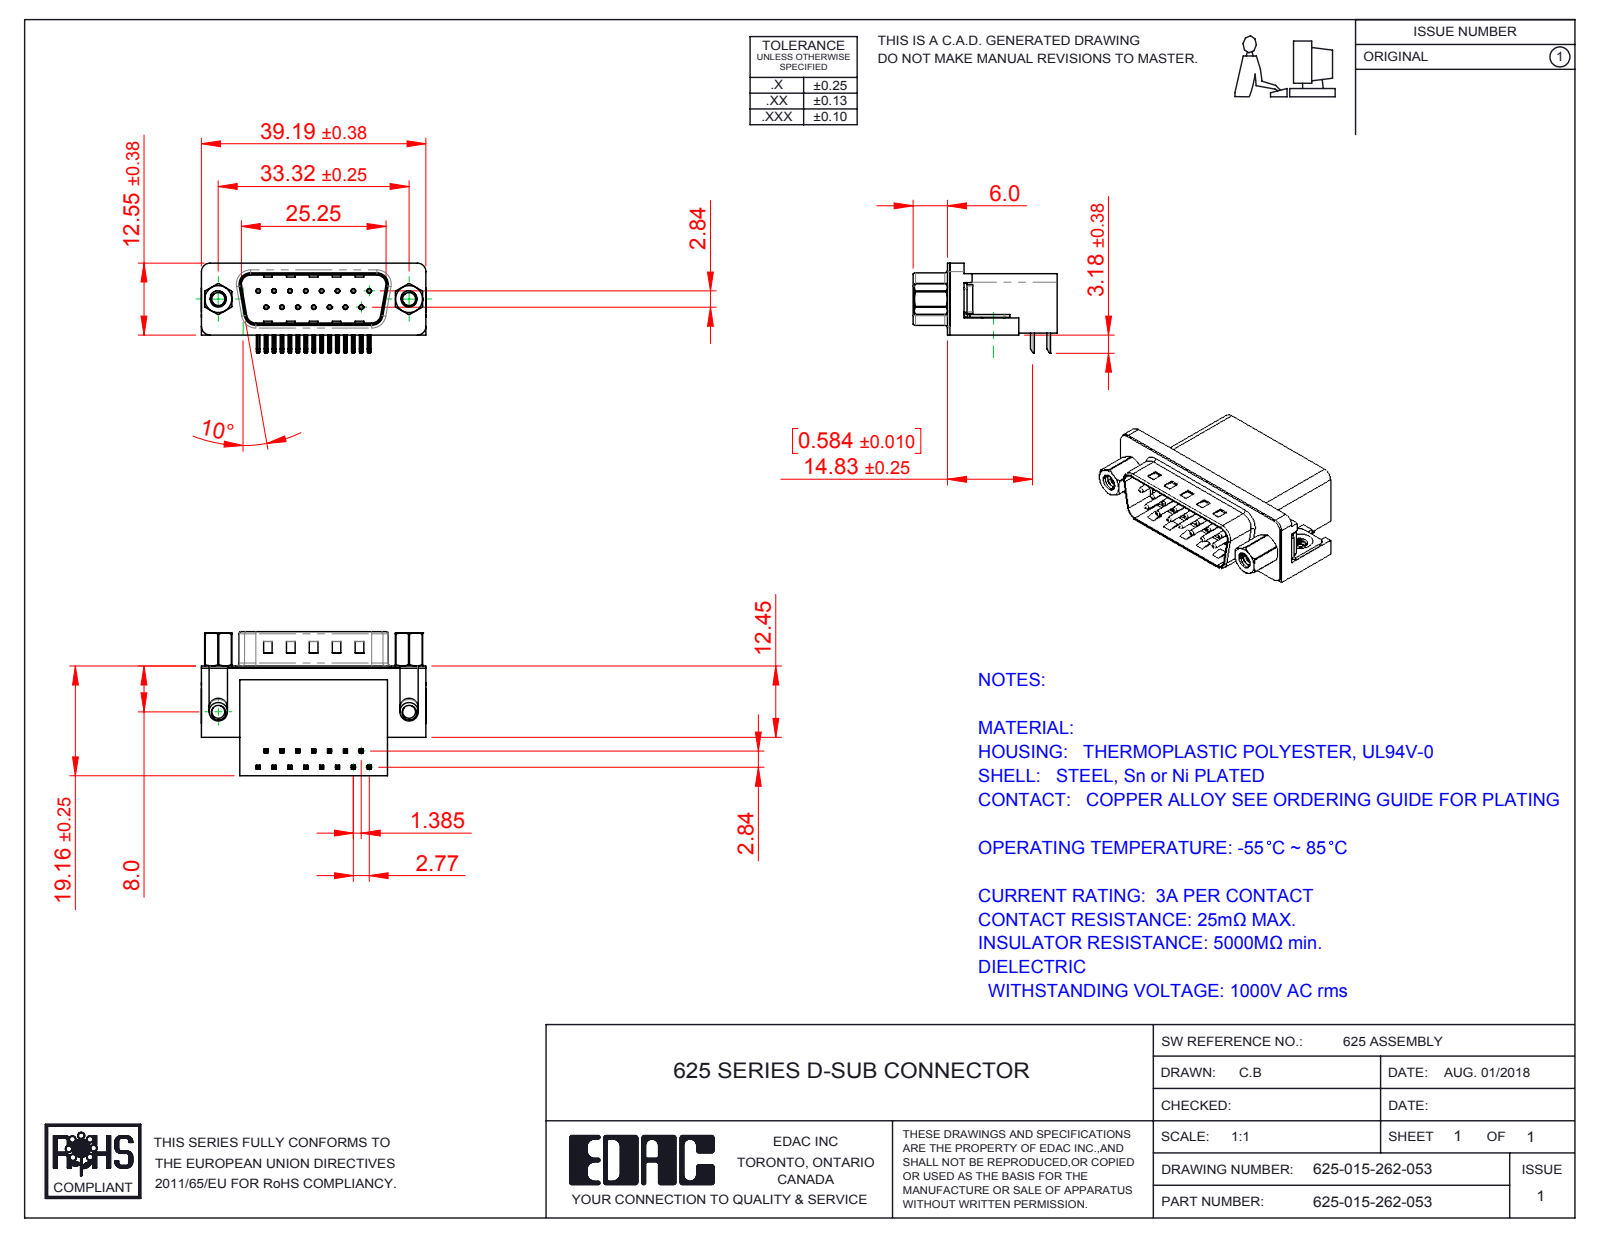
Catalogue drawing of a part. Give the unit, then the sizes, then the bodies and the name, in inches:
Units: inches
Overall size (bounding box): 1.544 × 0.991 × 0.619
Round holes (diameter × count): ⌀0.014 ×15, ⌀0.031 ×15, ⌀0.089 ×4, ⌀0.09 ×2, ⌀0.157 ×2, ⌀0.189 ×2, ⌀0.197 ×2
Round bosses / shafts (diameter × count): ⌀0.03 ×15, ⌀0.193 ×2, ⌀0.187 ×2, ⌀0.154 ×2, ⌀0.128 ×2, ⌀0.11 ×2
Partial cylindrical surfaces — rounded edges, fillets, slot ends (radius × count): R0.01 ×68, R0.005 ×30, R0.039 ×16, R0.02 ×9, R0.063 ×8, R0.059 ×6, R0.035 ×4, R0.079 ×4
Main face-to-face distances: 0.016, 0.407, 0.739, 0.083, 0.754, 0.412, 0.067, 0.428, 0.345, 0.64
Hole centre spacings: 0.124, 0.109, 0.218, 0.327, 0.436, 0.198, 0.198, 0.294
Volume: 0.395 in³ · Surface area: 10.83 in²
Bodies: 23 solids, 1637 faces (917 planar, 531 cylindrical, 189 other)
Part name (STEP PRODUCT): 625 Housing_15 Socket; 625 4-40 Threaded Board Mount; 625-015-262-053; 625 4-40 Hex Standoff 5 (+4 more)
STEP written by: SolidWorks 2016 (CONFIG_CONTROL_DESIGN)
